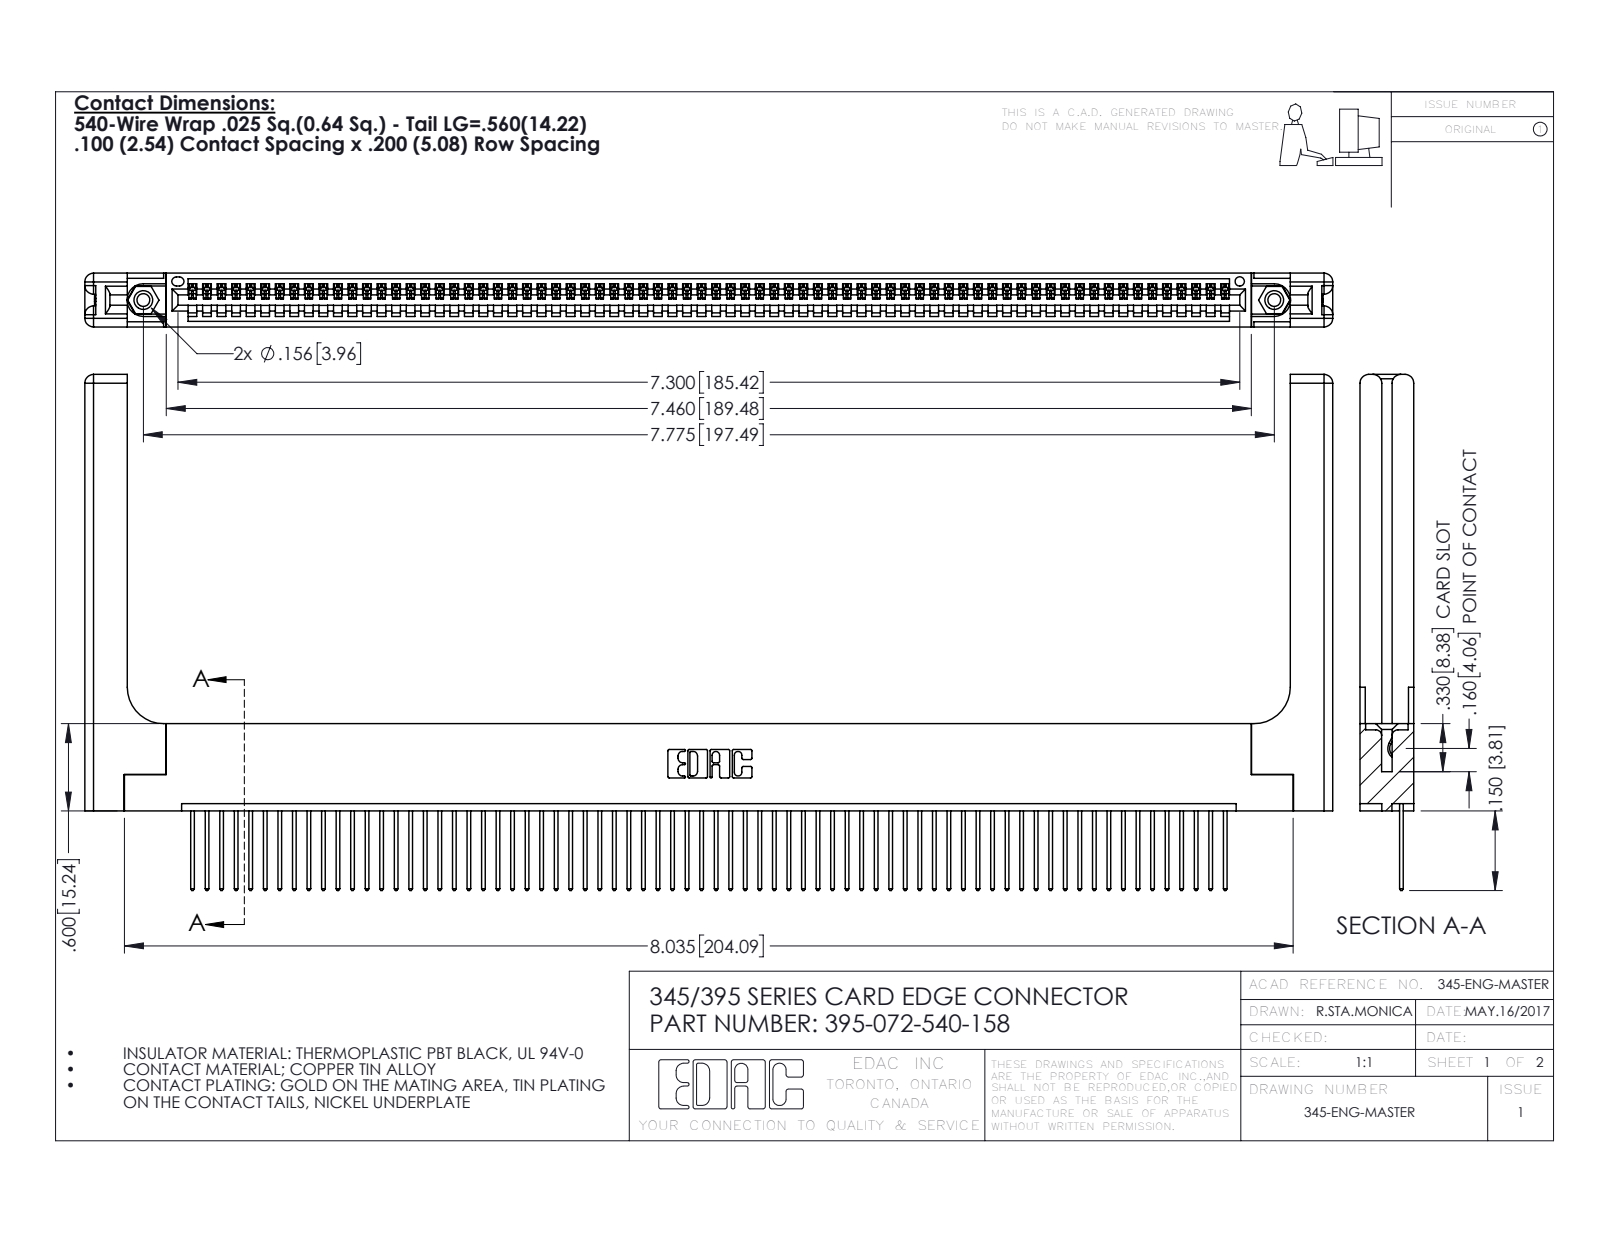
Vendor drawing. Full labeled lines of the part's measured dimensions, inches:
Part name (STEP PRODUCT): 345 Part_Flush Mounting Lugs - 0.156 Dia-TH; 345-250-001_345-250-001-102; 345-220-058_345-220-058; 345-292-001_345-293-140 (+1 more)
STEP written by: SolidWorks 2016 (CONFIG_CONTROL_DESIGN)
Units: inches
Bodies: 77 solids, 4558 faces (3108 planar, 1390 cylindrical, 60 other)
Overall size (bounding box): 8.579 × 3.547 × 0.37
Volume: 1.803 in³ · Surface area: 53.28 in²
Round holes (diameter × count): ⌀0.089 ×2, ⌀0.125 ×2, ⌀0.156 ×2, ⌀0.064 ×1
Round bosses / shafts (diameter × count): ⌀0.155 ×2
Partial cylindrical surfaces — rounded edges, fillets, slot ends (radius × count): R0.006 ×144, R0.01 ×144, R0.01 ×22, R0.06 ×16, R0.007 ×6, R0.031 ×6, R0.026 ×3, R0.03 ×2
Main face-to-face distances: 0.072, 0.298, 0.37, 0.098, 0.272, 0.025, 0.2, 0.225, 0.148, 0.15
Hole centre spacings: 0.27, 7.539, 7.775
